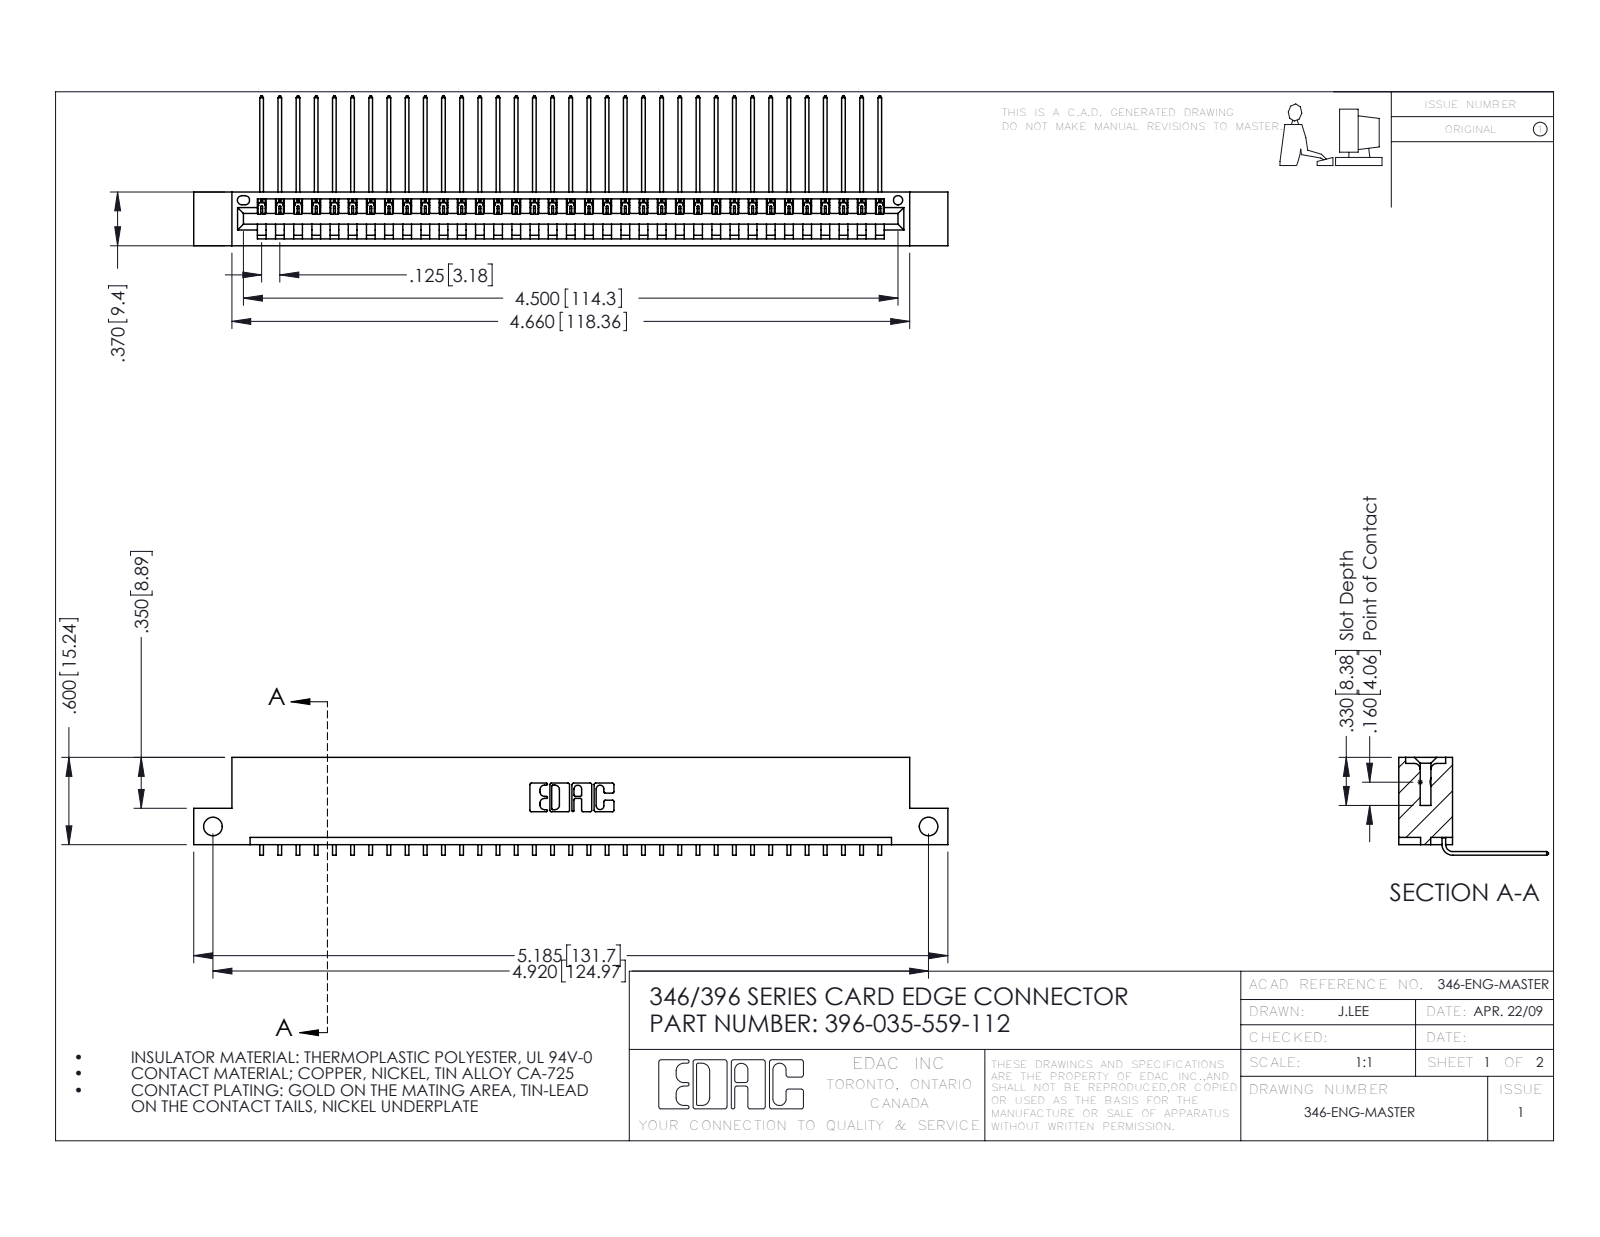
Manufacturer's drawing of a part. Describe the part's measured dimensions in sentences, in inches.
The part is named "345-292-001_558 559 Tail - 1; 396-035-559-112; 346 Part_Flush Mounting Lugs - Side Mount". Its 3-D file was written by "SolidWorks 2016 (CONFIG_CONTROL_DESIGN)". It is 36 solids with 2222 faces: 1546 planar, 676 cylindrical and 0 other. Overall it measures 5.185 by 1.03 by 0.673 inches. Its volume is 0.768 cubic inches and its surface area 25.12 square inches. Round holes: 2 of diameter 0.128, 1 of diameter 0.064. Partial cylindrical surfaces (rounded edges, fillets, slot ends): 70 of radius 0.006, 22 of radius 0.01, 6 of radius 0.007, 6 of radius 0.031, 3 of radius 0.026, 2 of radius 0.031, 2 of radius 0.04, 1 of radius 0.014. The main face-to-face distances are 0.048, 0.322, 0.37, 0.25, 0.072, 0.025, 0.298, 0.148, 0.222, 0.1. The hole center spacings are 4.92.
